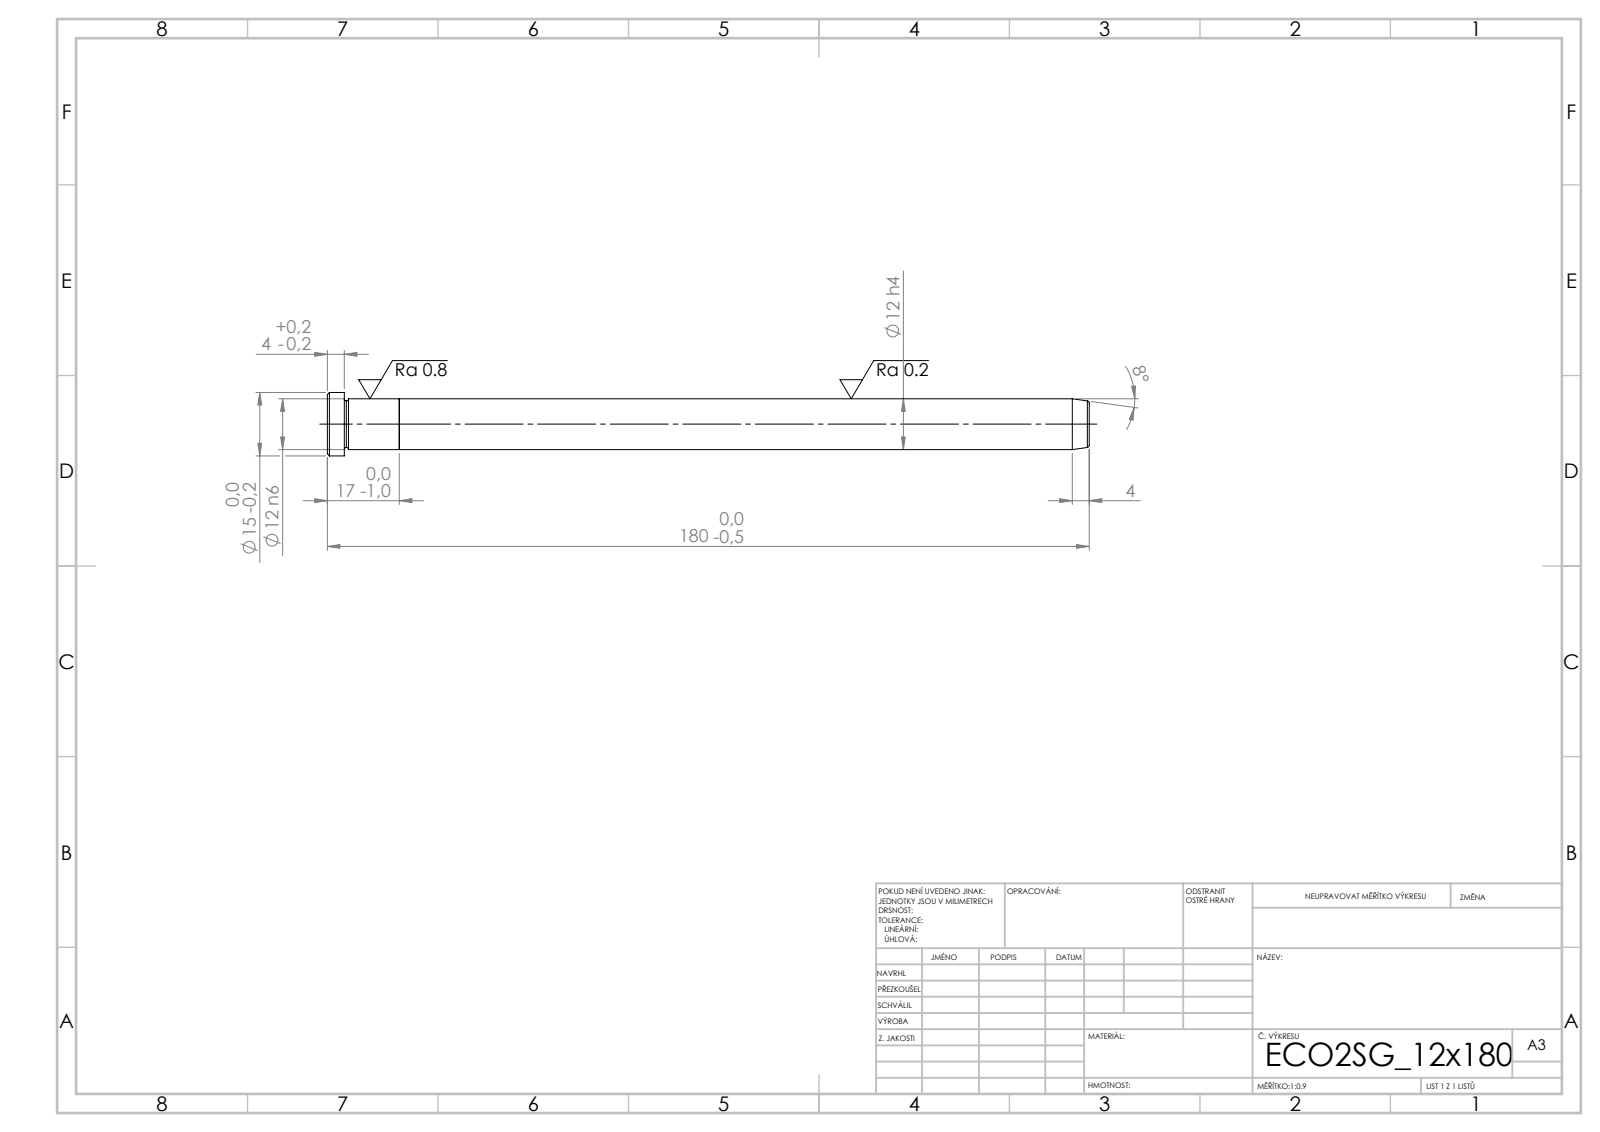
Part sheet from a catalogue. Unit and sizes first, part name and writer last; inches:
Units: inches
Overall size (bounding box): 7.087 × 0.591 × 0.591
Round bosses / shafts (diameter × count): ⌀0.591 ×1, ⌀0.472 ×1
Main face-to-face distances: 0.669, 6.417, 7.087, 6.929, 0.512, 0.157
Volume: 1.254 in³ · Surface area: 11.43 in²
Bodies: 2 solids, 21 faces (5 planar, 6 cylindrical, 10 other)
STEP written by: SolidWorks 2019 (CONFIG_CONTROL_DESIGN)
